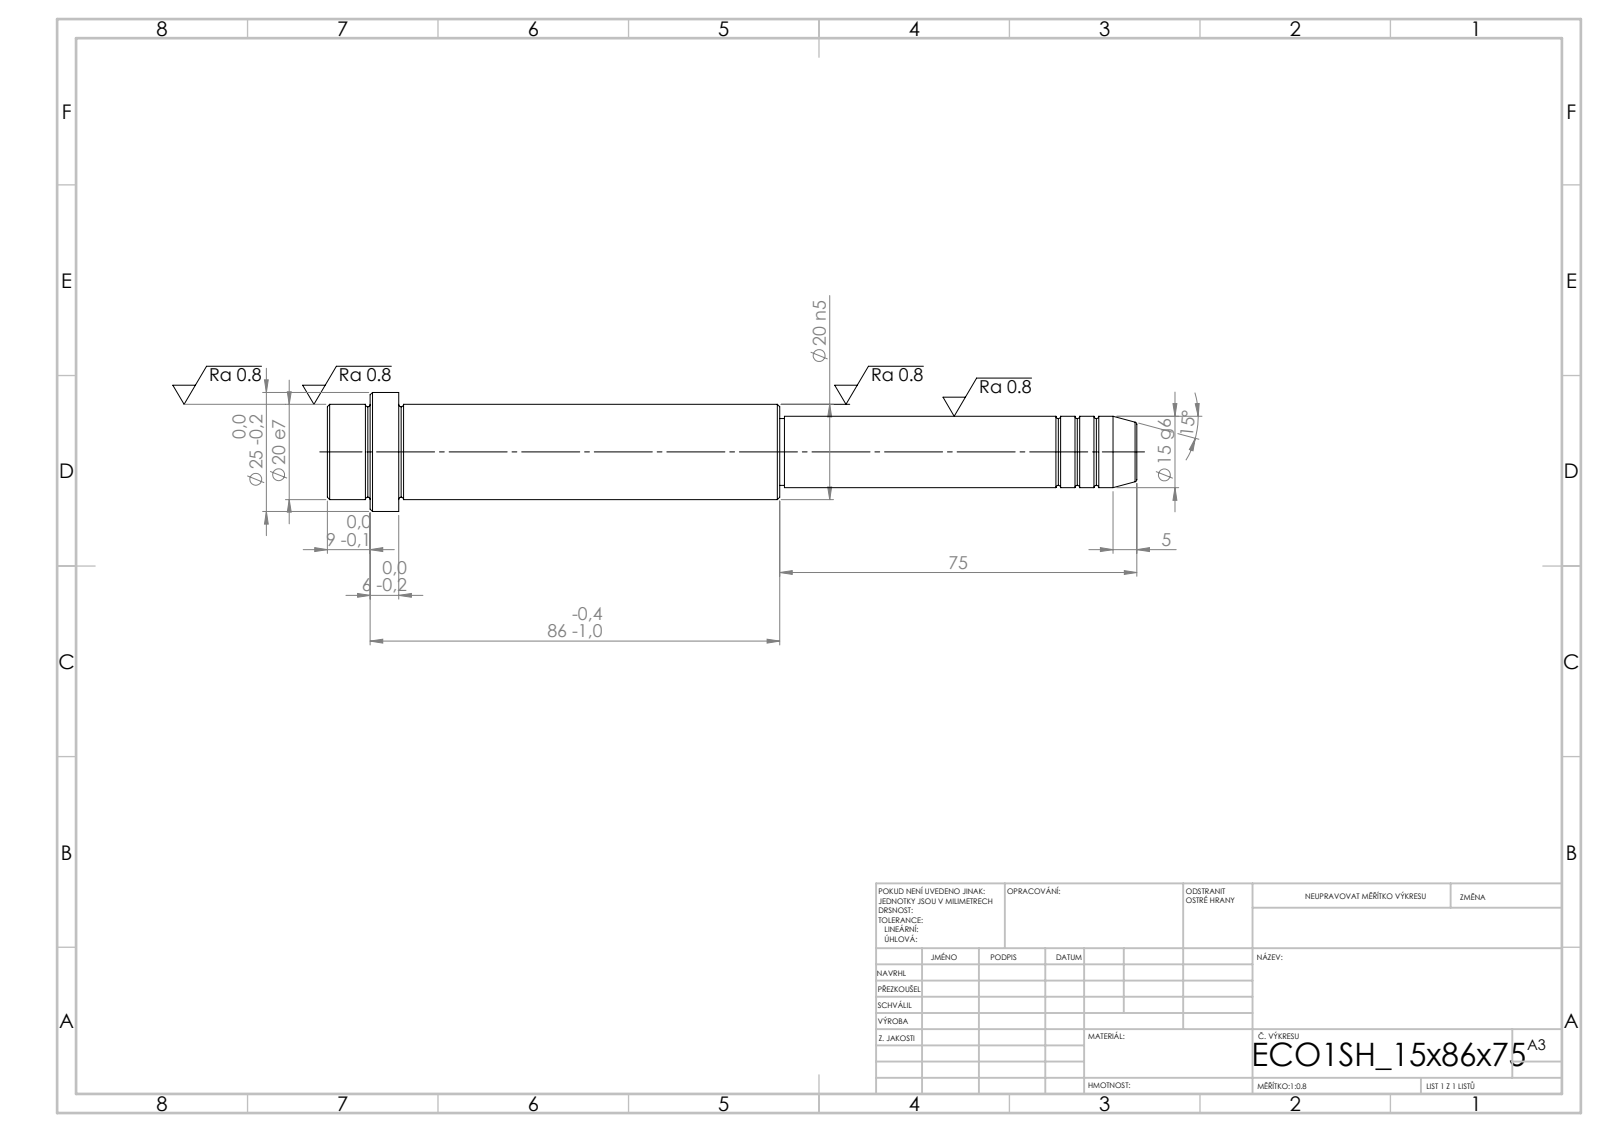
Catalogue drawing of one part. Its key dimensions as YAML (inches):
step_written_by: "SolidWorks 2019 (CONFIG_CONTROL_DESIGN)"
units: inches
bodies: {solids: 1, faces: 52, planar: 6, cylindrical: 16, other: 30}
overall_size: [6.693, 0.984, 0.984]
volume: 2.676
surface_area: 16.46
round_bosses_or_shafts:
  - {diameter: 0.984, count: 1}
  - {diameter: 0.787, count: 1}
  - {diameter: 0.591, count: 1}
  - {diameter: 0.551, count: 1}
face_to_face_distances: [0.591, 0.236, 0.354, 3.15, 3.386, 3.74, 2.953, 6.102, 6.339, 6.693]
